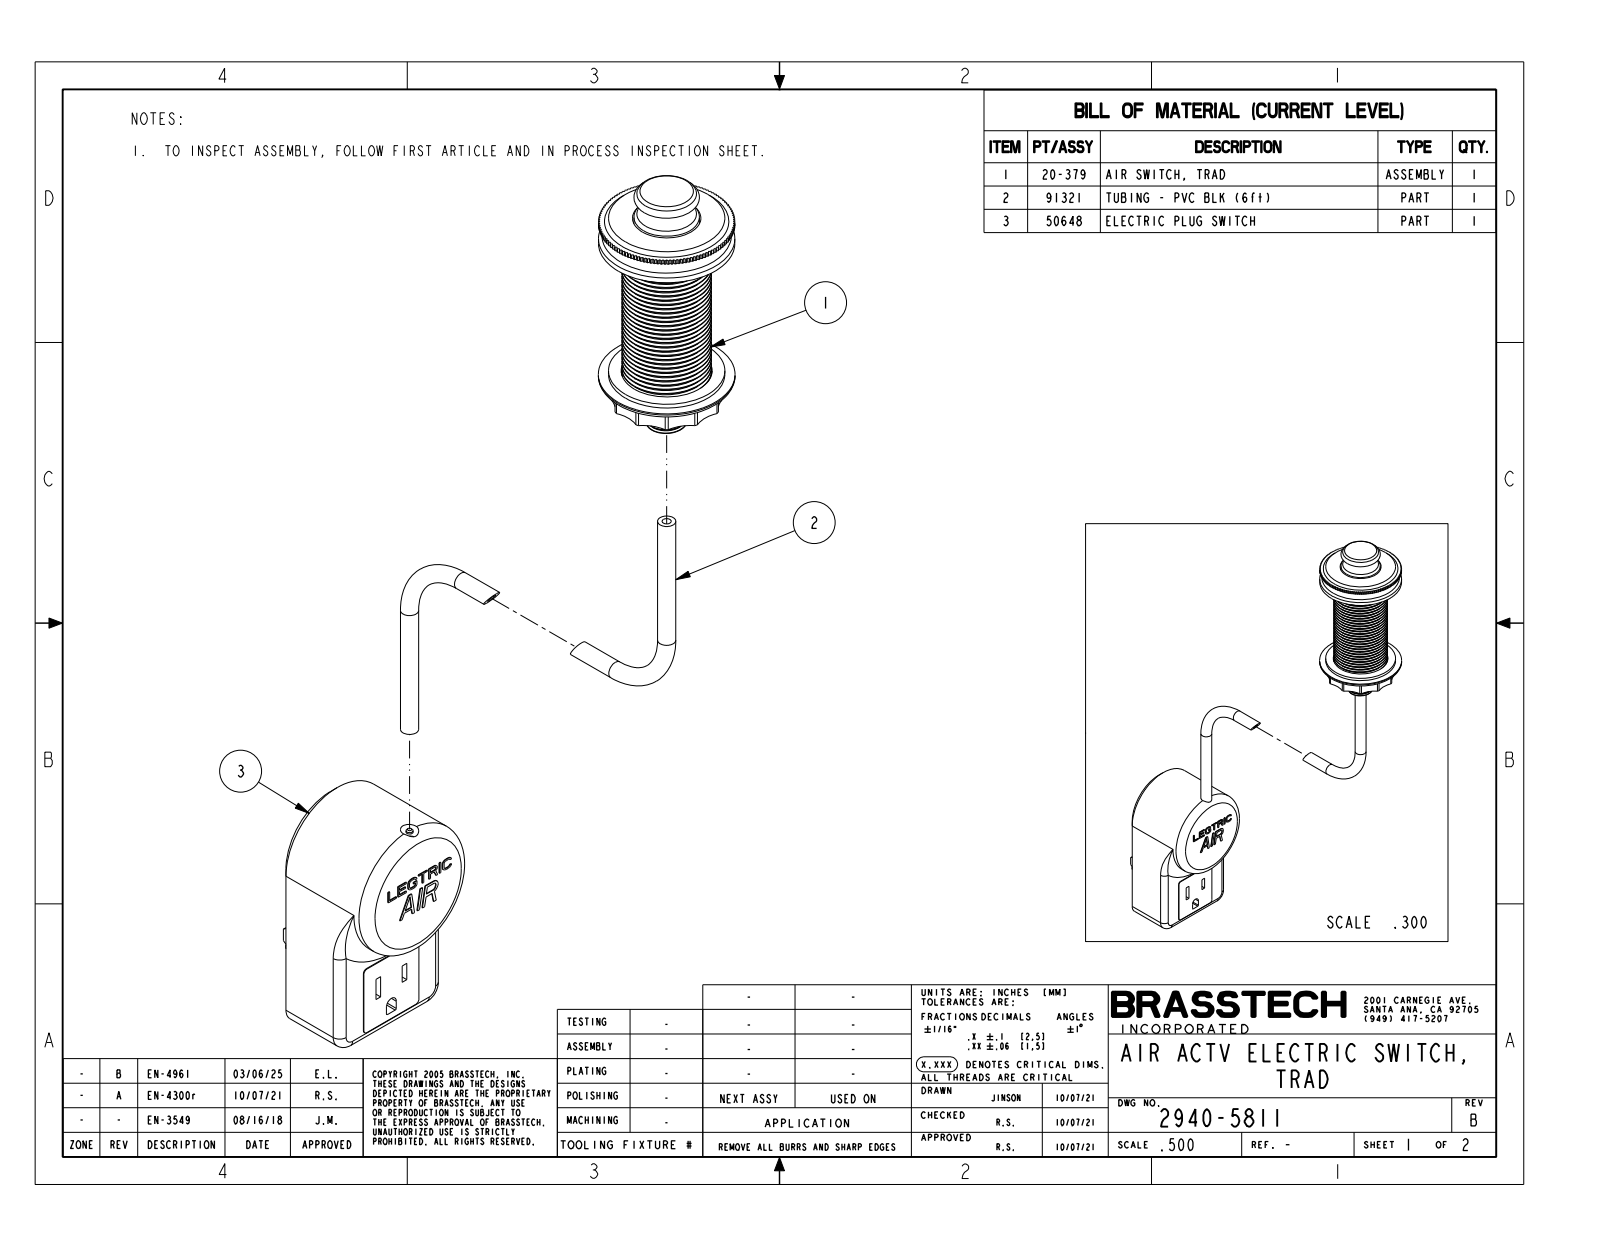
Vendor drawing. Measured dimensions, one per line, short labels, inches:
name: 2940-5811
written by: CREO PARAMETRIC BY PTC INC, 2018400 (AUTOMOTIVE_DESIGN)
unit: in
bodies: 3 solids, 843 faces (496 planar, 273 cylindrical, 74 other)
size: 12.984 × 8.313 × 1.99
volume: 14.06 in³; area: 70.24 in²
holes: 4× ⌀0.125, 1× ⌀0.65, 1× ⌀0.94, 1× ⌀1.25
bosses: 3× ⌀0.25, 1× ⌀1.99, 1× ⌀1.88, 1× ⌀1.875, 1× ⌀1.779, 1× ⌀1.6, 1× ⌀1.23, 1× ⌀1.153
rounds: 12× R0.5, 4× R0.06, 3× R0.125, 2× R0.02, 2× R0.25, 1× R0.095, 1× R0.81
face distances: 1.99, 1.7, 0.08, 0.36, 12.059, 0.52, 12.484, 0.425, 1.18, 0.44
hole spacings: 5
